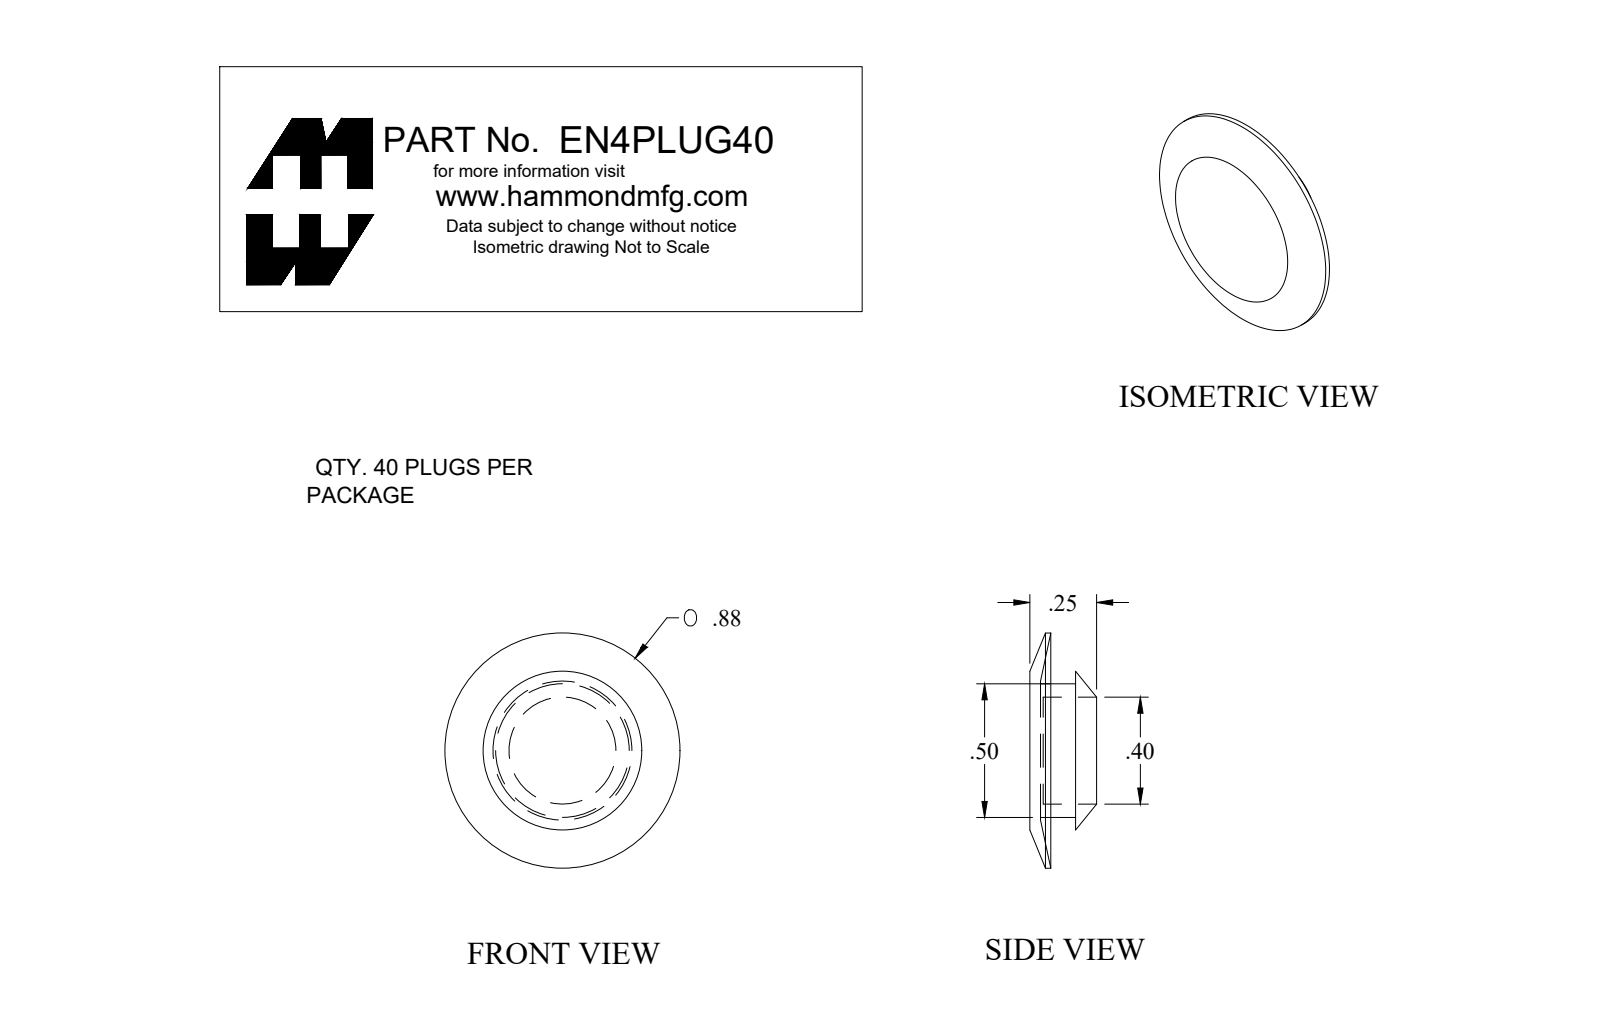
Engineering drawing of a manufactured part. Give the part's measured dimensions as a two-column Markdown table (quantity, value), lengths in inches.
| quantity | value |
| --- | --- |
| part name | EN4PLUG40 |
| STEP written by | SolidWorks 2019 (AUTOMOTIVE_DESIGN) |
| units | inches |
| bodies | 1 solid, 10 faces (4 planar, 3 cylindrical, 3 other) |
| overall size | 0.88 × 0.88 × 0.25 |
| volume | 0.038 in³ |
| surface area | 1.97 in² |
| round holes (diameter × count) | 0.4 × 1 |
| round bosses / shafts (diameter × count) | 0.88 × 1, 0.5 × 1 |
| main face-to-face distances | 0.05, 0.171, 0.121, 0.04, 0.131 |
